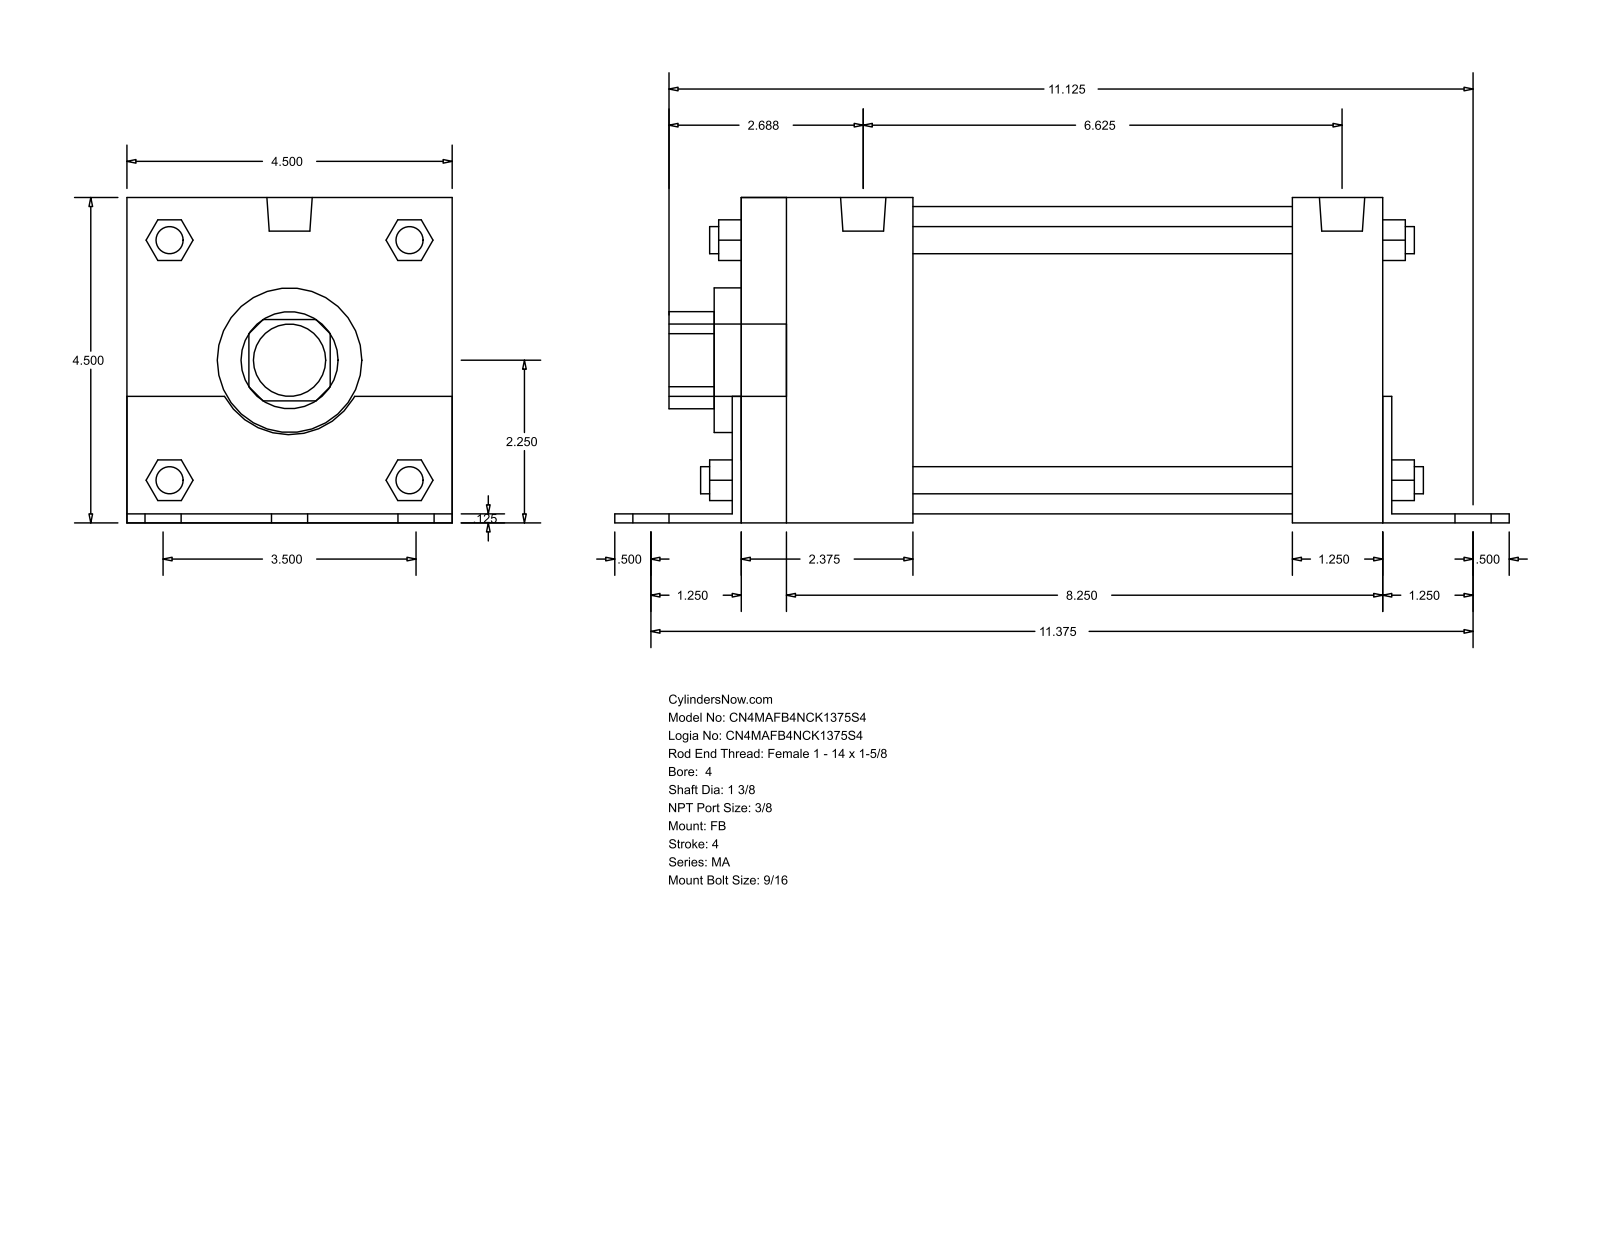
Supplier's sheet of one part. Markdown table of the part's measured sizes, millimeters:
| quantity | value |
| --- | --- |
| part name | MA_FB__0400_1.375 |
| STEP written by | GSSL Pune (CONFIG_CONTROL_DESIGN) |
| units | millimeters |
| bodies | 0 solids, 140 faces (105 planar, 35 cylindrical, 0 other) |
| overall size | 314.32 × 114.35 × 114.3 |
| round holes (diameter × count) | 34.92 × 1, 50.8 × 1, 107.95 × 1 |
| round bosses / shafts (diameter × count) | 14.29 × 6, 11.11 × 4, 9.53 × 4, 15.93 × 2, 25.4 × 1 |
| partial cylindrical surfaces (radius × count) | 17.06 × 1, 26.16 × 1 |
| main face-to-face distances | 114.3, 3.17, 114.35, 3.12, 111.18, 225.42, 3.18, 228.6, 34.93, 60.32 |
